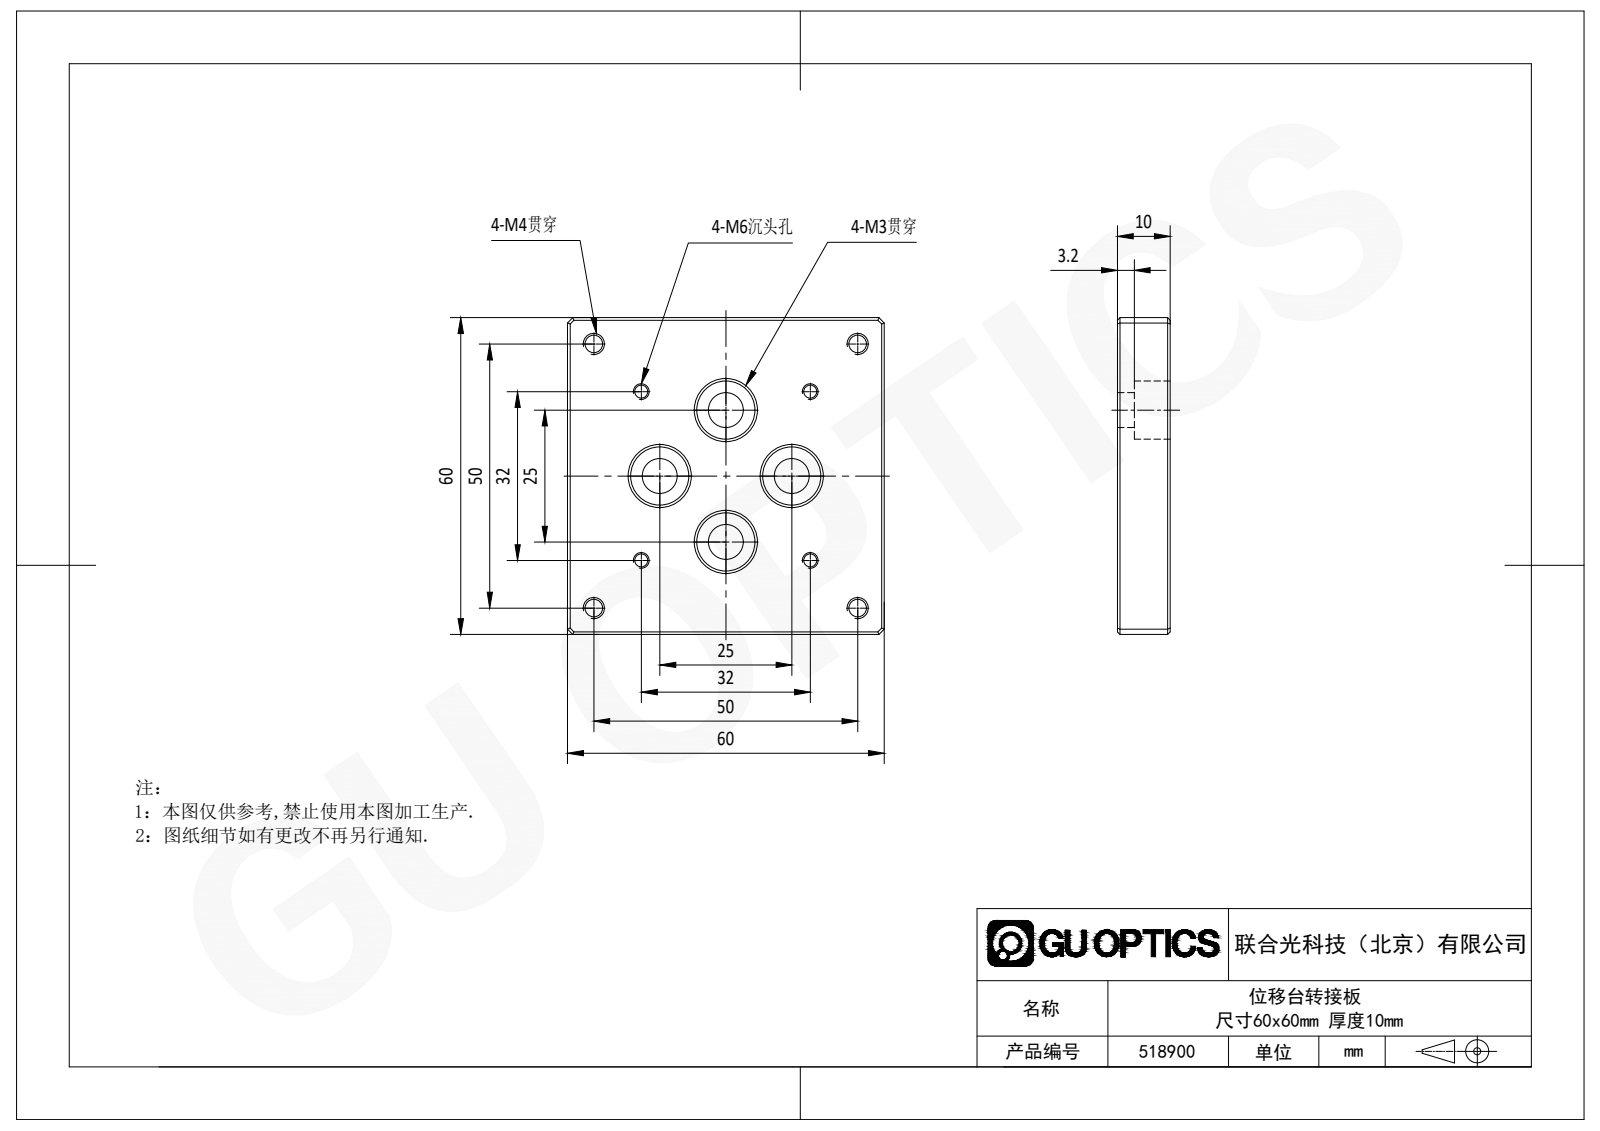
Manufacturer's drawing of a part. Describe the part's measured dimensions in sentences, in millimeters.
Its 3-D file was written by "SolidWorks 2020 (CONFIG_CONTROL_DESIGN)". It is 1 solid with 58 faces: 30 planar, 16 cylindrical and 12 other. Overall it measures 60 by 60 by 10 millimeters. Its volume is 32 334 cubic millimeters and its surface area 10 930 square millimeters. Round holes: 4 of diameter 2.5, 4 of diameter 3.3, 4 of diameter 6.6, 4 of diameter 11. The main face-to-face distances are 10, 60, 3.2, 6.8, 48.79, 83.42, 65.37. The hole center spacings are 16.38, 27.95, 32.68, 41.98, 45.07, 12.73, 17.68, 32.
